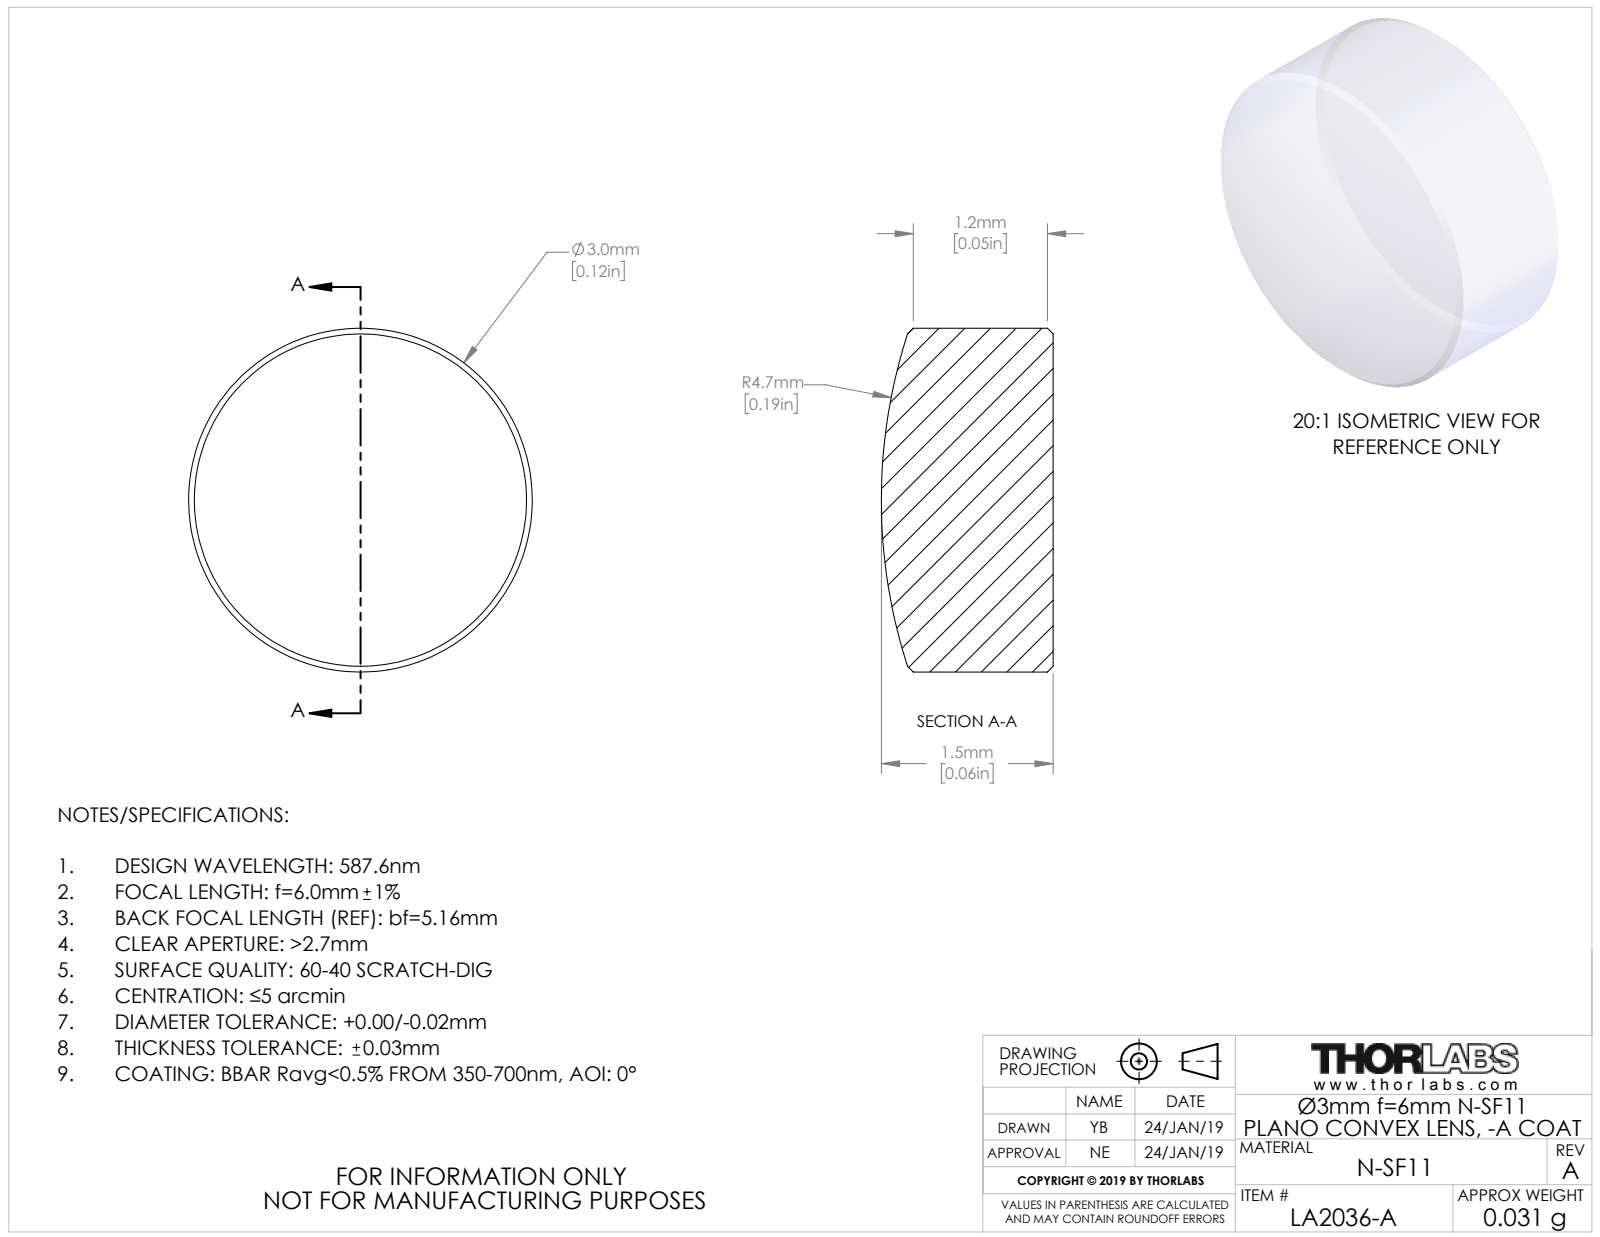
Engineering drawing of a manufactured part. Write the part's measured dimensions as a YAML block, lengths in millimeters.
part_name: "TTN162749-E0W"
step_written_by: "SolidWorks 2018 (CONFIG_CONTROL_DESIGN)"
units: millimeters
bodies: {solids: 1, faces: 9, planar: 1, cylindrical: 2, other: 6}
overall_size: [3, 3, 1.5]
volume: 10
surface_area: 26
round_bosses_or_shafts:
  - {diameter: 3, count: 1}
